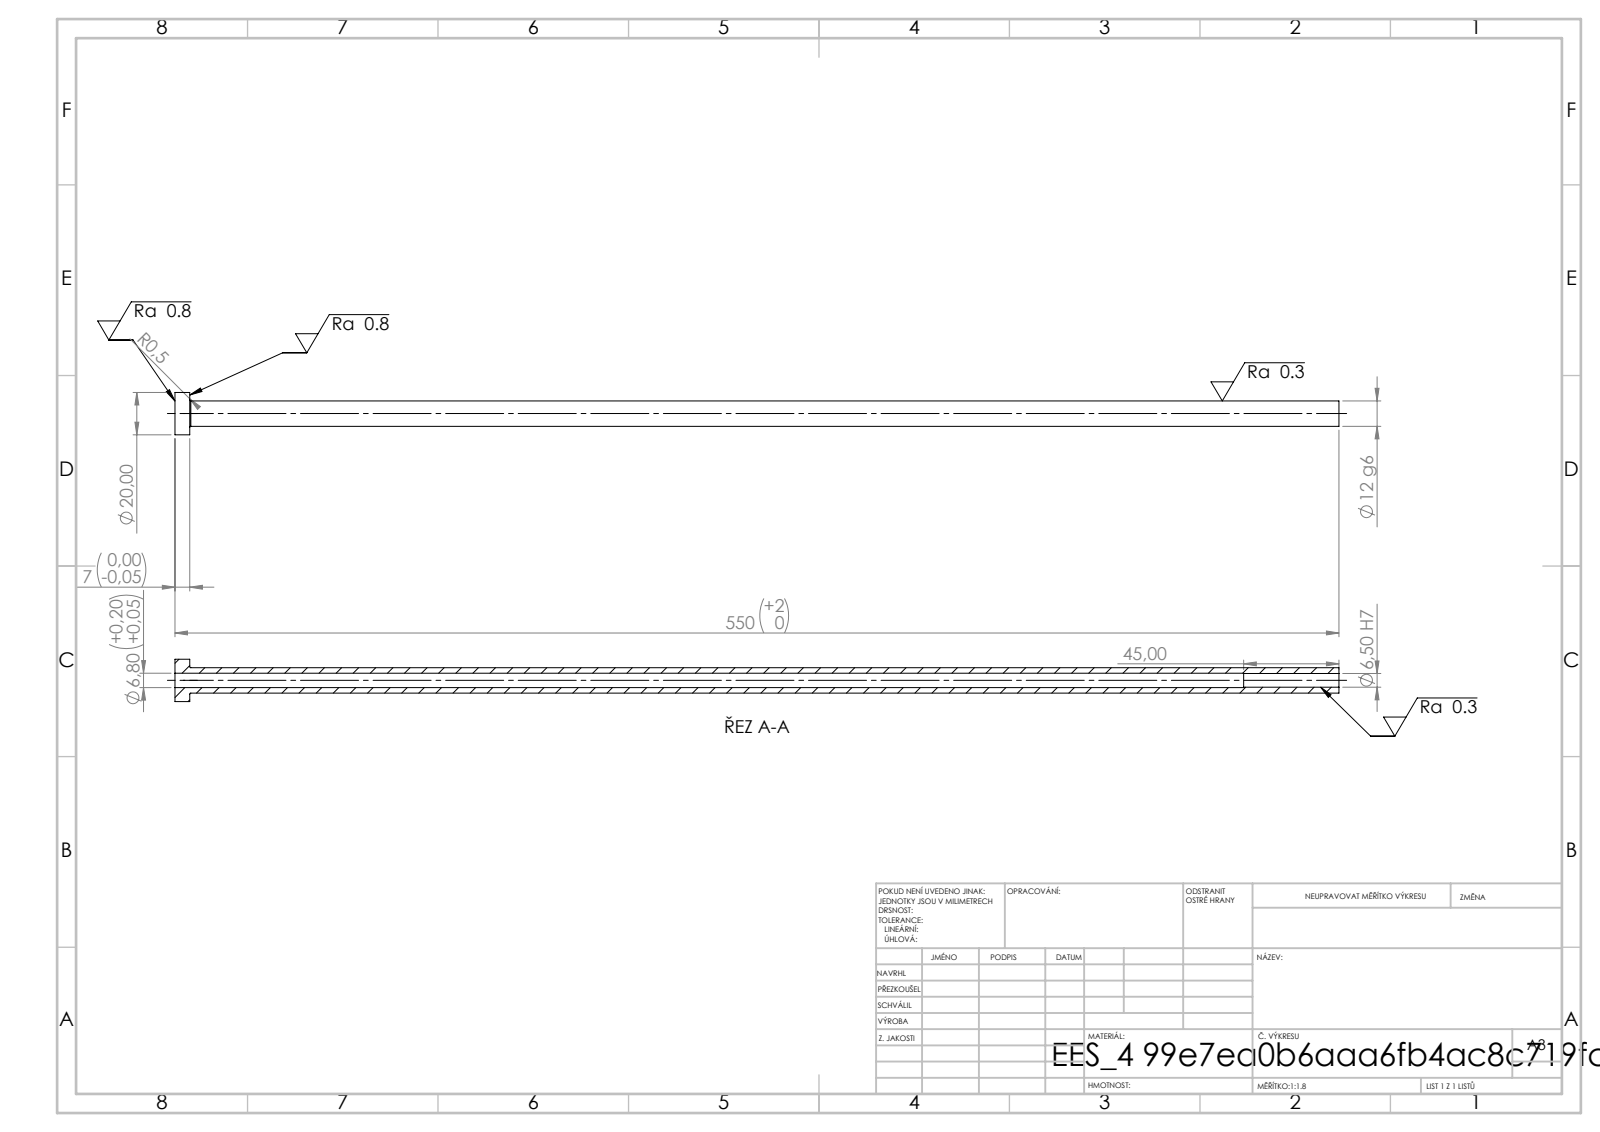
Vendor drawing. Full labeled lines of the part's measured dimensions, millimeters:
STEP written by: SolidWorks 2019 (CONFIG_CONTROL_DESIGN)
Units: millimetres
Bodies: 1 solid, 14 faces (4 planar, 8 cylindrical, 2 other)
Overall size (bounding box): 550 × 20 × 20
Volume: 43 780 mm³ · Surface area: 33 172 mm²
Round holes (diameter × count): ⌀6.5 ×1, ⌀6.8 ×1
Round bosses / shafts (diameter × count): ⌀20 ×1, ⌀12 ×1
Main face-to-face distances: 7, 550, 543, 505, 498, 45
